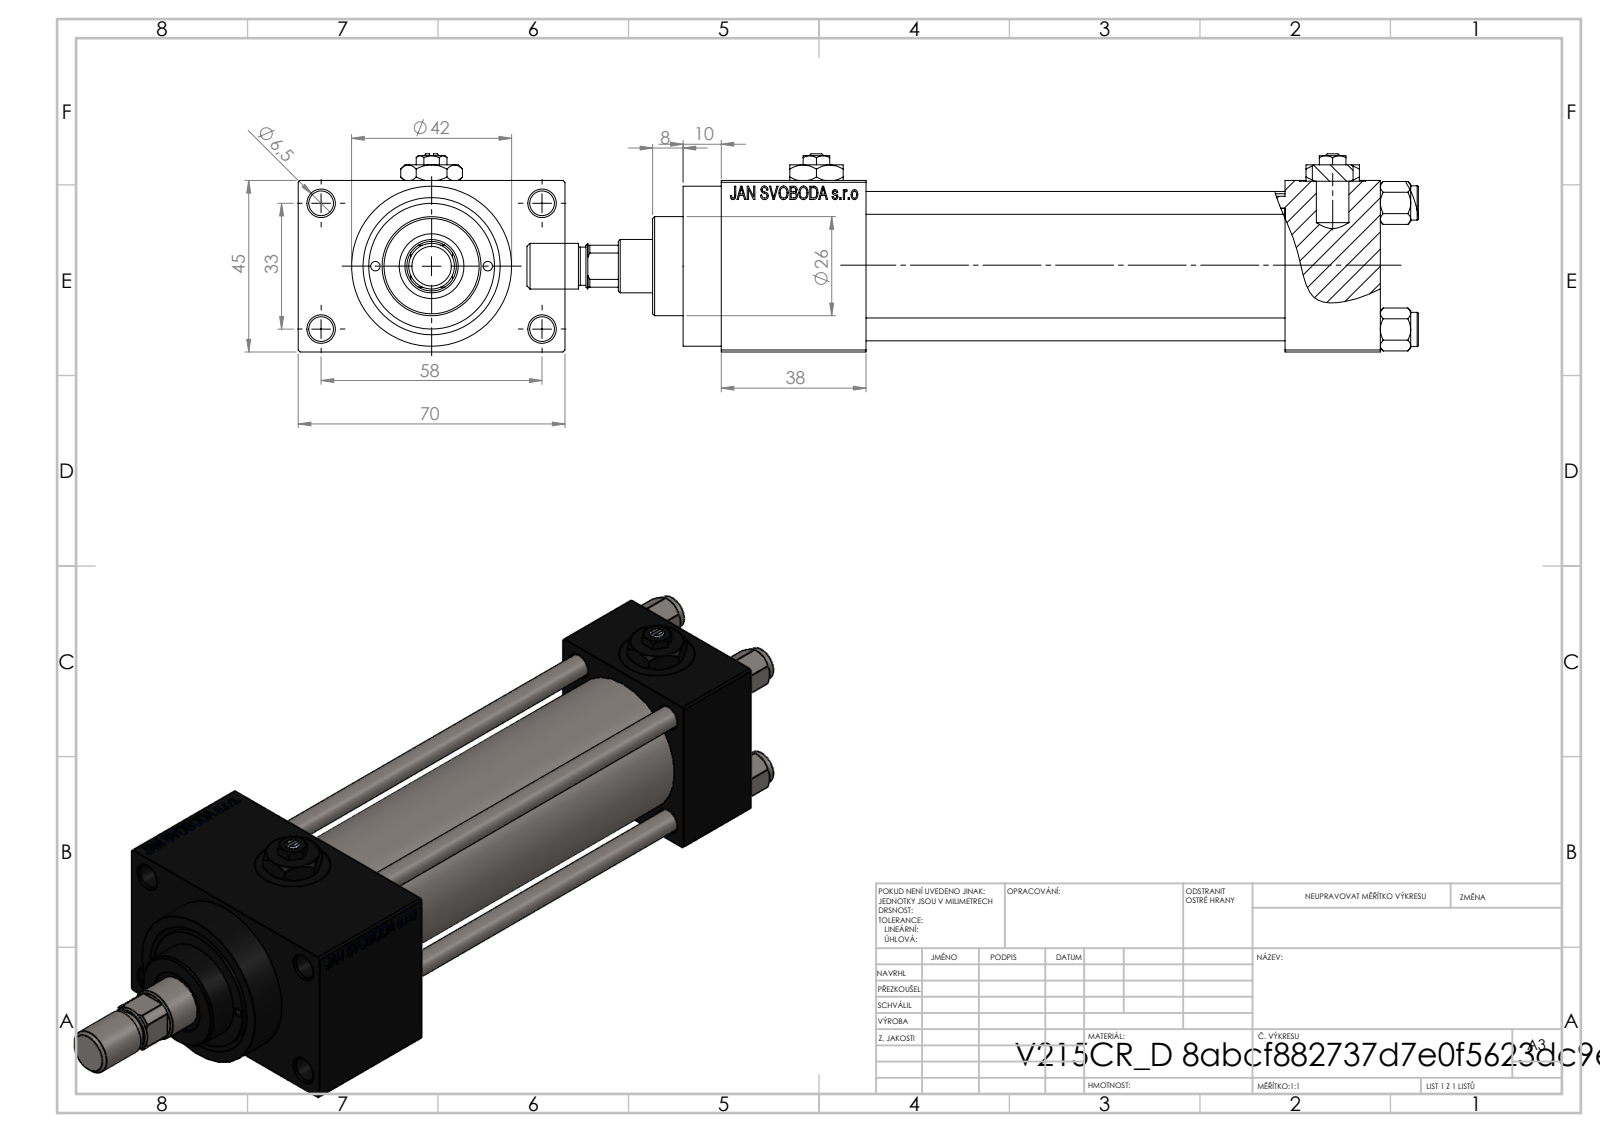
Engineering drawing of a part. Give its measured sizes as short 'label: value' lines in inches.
name: V215CR_D_Body; V215CR_VCP_D; Zatka_pro_OIL_PORT; ROD_END_AH (+3 more)
written by: SolidWorks 2019 (CONFIG_CONTROL_DESIGN)
unit: in
bodies: 14 solids, 1223 faces (548 planar, 107 cylindrical, 568 other)
size: 9.213 × 2.756 × 2.047
volume: 16.26 in³; area: 152.4 in²
holes: 5× ⌀0.256, 4× ⌀0.236, 4× ⌀0.518, 4× ⌀0.787, 3× ⌀0.276, 2× ⌀0.098, 1× ⌀0.551, 1× ⌀0.669, 1× ⌀0.945, 1× ⌀1.26, 1× ⌀1.299
bosses: 4× ⌀0.354, 1× ⌀1.654, 1× ⌀1.496, 1× ⌀1.024, 1× ⌀0.472, 1× ⌀0.394
rounds: 1× R0.256
face distances: 1.772, 0.984, 0.492, 4.331, 5.315, 2.264, 5.827, 1.496, 6.811, 2.756
hole spacings: 0.488, 0.657, 0.858, 0.924, 1.307, 1.314, 1.392, 1.396
